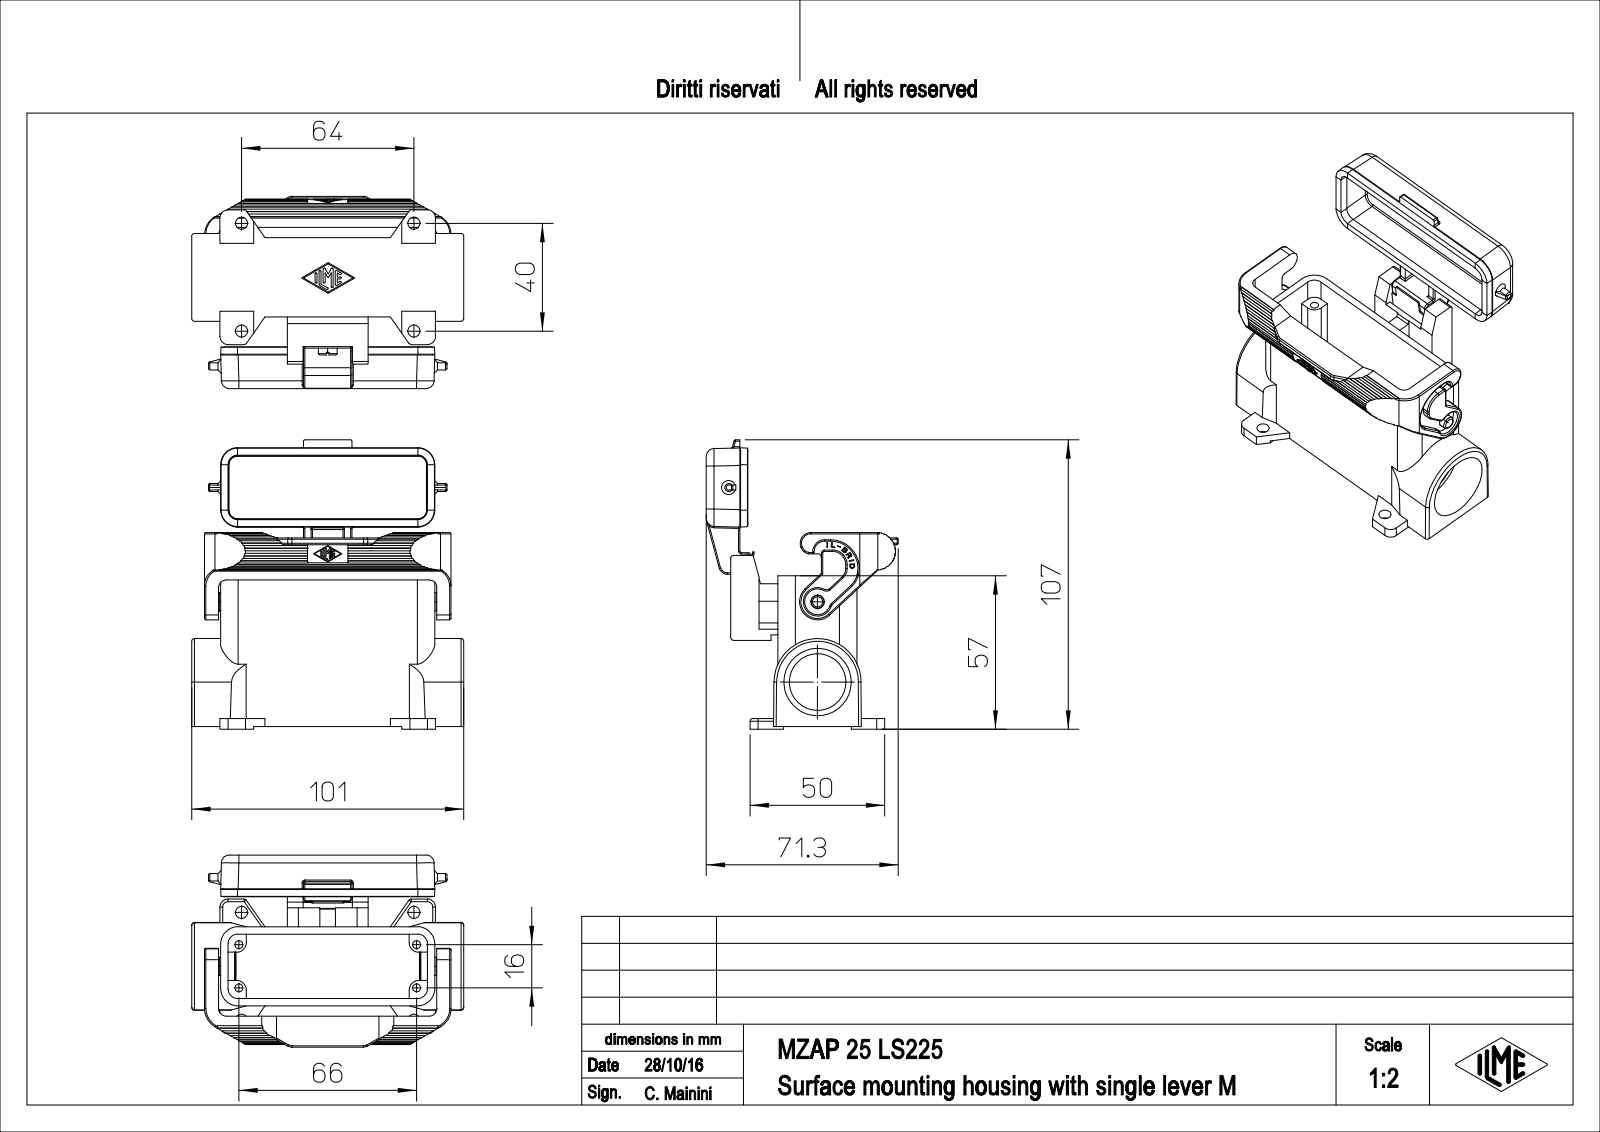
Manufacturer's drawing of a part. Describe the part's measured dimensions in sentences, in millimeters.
The part is named "MZAP_25_LS225". Its 3-D file was written by "PTC Creo Elements/Direct Modeling 19.0E 27-Jun-2016 (C) Parametric Technology GmbH (AUTOMOTIVE_DESIGN)". It is 1 solid with 994 faces: 603 planar, 287 cylindrical and 104 other. Overall it measures 107.4 by 101 by 71.3 millimeters. Its volume is 88 594 cubic millimeters and its surface area 55 949 square millimeters. Round holes: 4 of diameter 3, 4 of diameter 4.5, 1 of diameter 5, 1 of diameter 21, 1 of diameter 25. Round bosses or shafts: 1 of diameter 7, 1 of diameter 6.8, 1 of diameter 4.8, 1 of diameter 3. Partial cylindrical surfaces (rounded edges, fillets, slot ends): 72 of radius 0.5, 15 of radius 0.2, 14 of radius 1, 12 of radius 3, 12 of radius 3.5, 8 of radius 6.5, 4 of radius 3.2, 4 of radius 5.3. The main face-to-face distances are 2.76, 26.64, 29.4, 23.88, 56, 2, 3, 54, 24.6, 27.36. The hole center spacings are 12.04, 28.02, 66.1, 70.77, 16, 40, 64, 66.
